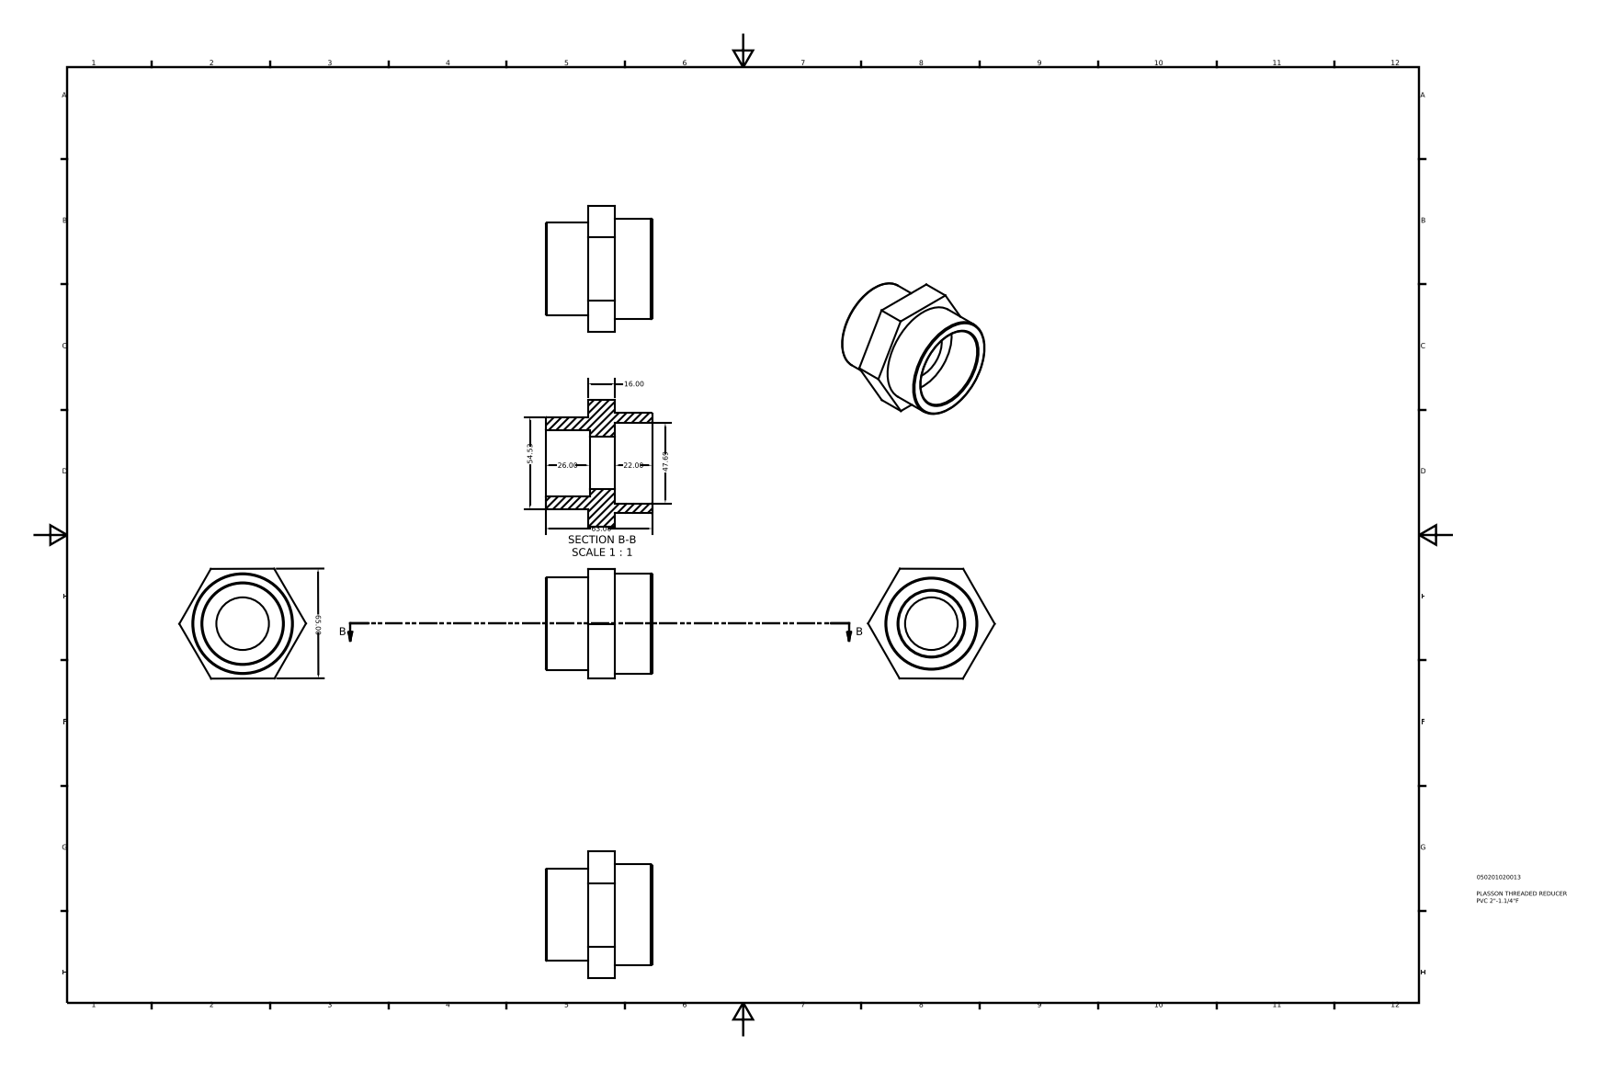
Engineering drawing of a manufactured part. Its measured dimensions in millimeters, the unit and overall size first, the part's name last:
Units: millimetres
Overall size (bounding box): 75.06 × 65.11 × 63
Round holes (diameter × count): ⌀31.16 ×1, ⌀38.95 ×1, ⌀47.69 ×1
Round bosses / shafts (diameter × count): ⌀59.61 ×1, ⌀54.53 ×1
Main face-to-face distances: 16, 65.04, 25, 41, 63, 38, 22, 65, 26, 1
Volume: 96 569 mm³ · Surface area: 25 583 mm²
Bodies: 1 solid, 21 faces (12 planar, 5 cylindrical, 4 other)
Part name (STEP PRODUCT): 050201020013
STEP written by: Autodesk Inventor 2015 (AUTOMOTIVE_DESIGN)
